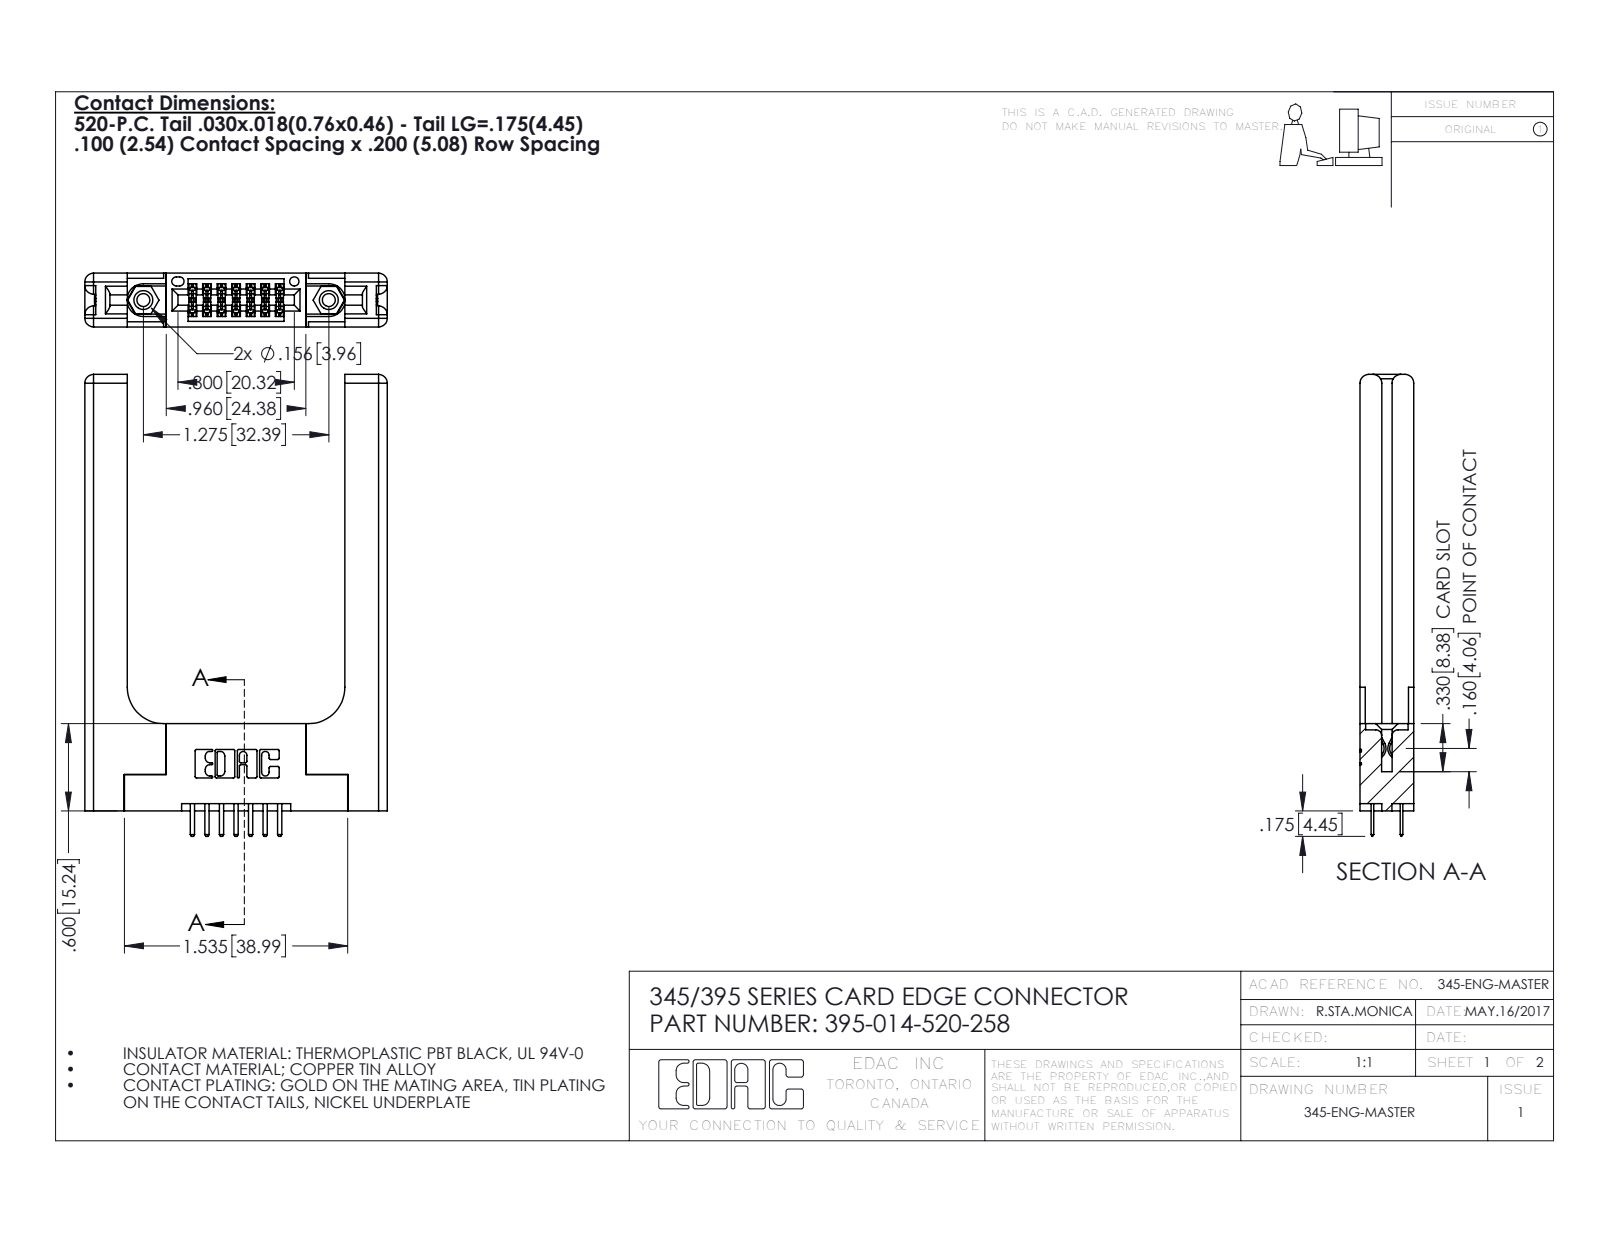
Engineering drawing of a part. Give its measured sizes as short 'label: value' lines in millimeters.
name: 345-250-001_345-250-001-102; 345-292-001_345-293-120; 345-220-058_345-220-058; 345 Part_Flush Mounting Lugs - 0.156 Dia-TH (+1 more)
written by: SolidWorks 2016 (CONFIG_CONTROL_DESIGN)
unit: mm
bodies: 19 solids, 1138 faces (718 planar, 360 cylindrical, 60 other)
size: 80.6 × 52.8 × 9.4
volume: 13 300 mm³; area: 11 460 mm²
holes: 2× ⌀2.3, 2× ⌀3.2, 2× ⌀4, 1× ⌀1.6
bosses: 2× ⌀3.9
rounds: 22× R0.3, 21× R0.2, 18× R0.3, 16× R1.5, 6× R0.2, 6× R0.8, 3× R0.7, 2× R0.4
face distances: 9.4, 3.8, 5.6, 1.8, 2, 7.6, 3.8, 38, 5.1, 1.8
hole spacings: 6.9, 26.5, 32.4
